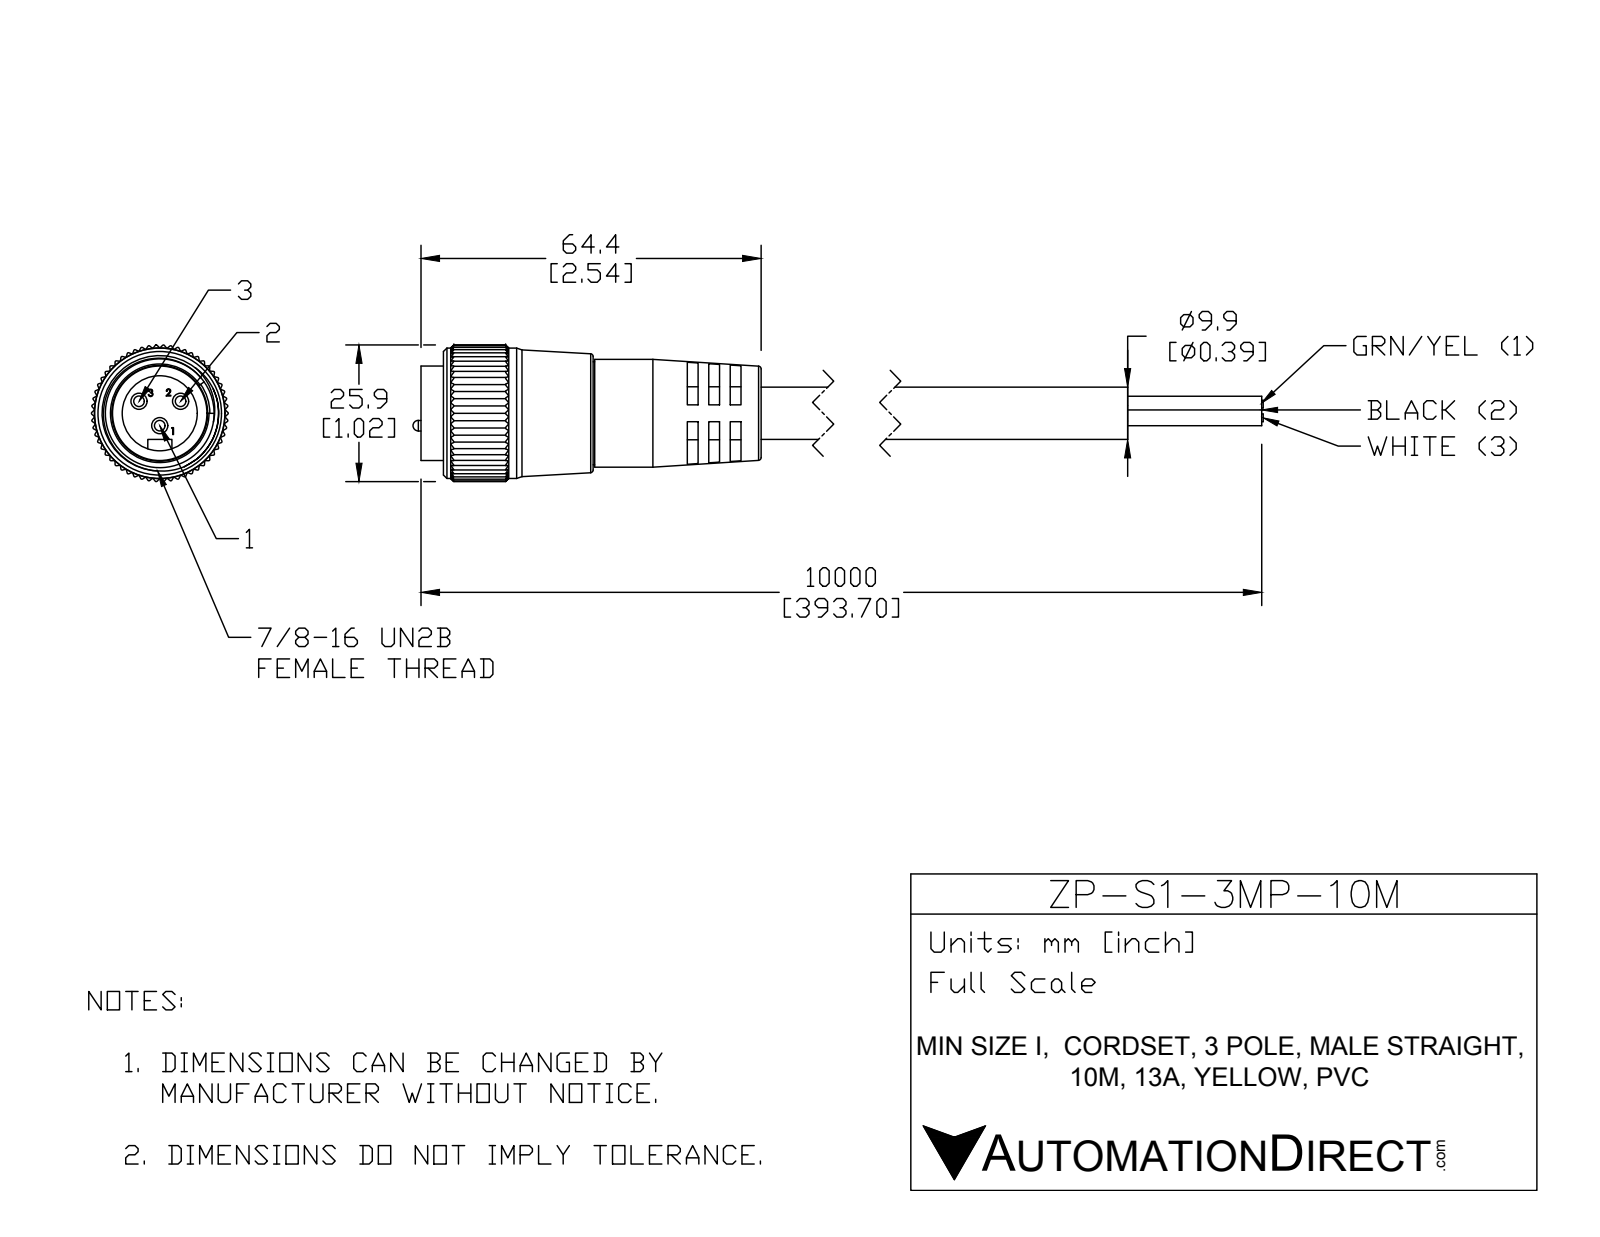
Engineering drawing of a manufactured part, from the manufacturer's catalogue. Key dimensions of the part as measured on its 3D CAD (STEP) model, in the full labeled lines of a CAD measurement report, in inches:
Part name (STEP PRODUCT): ZP-S1-3MP-10M
STEP written by: SolidWorks 2015 (AUTOMOTIVE_DESIGN)
Units: inches
Bodies: 5 solids, 564 faces (196 planar, 314 cylindrical, 54 other)
Overall size (bounding box): 4.316 × 2.083 × 1.017
Volume: 1.648 in³ · Surface area: 19.55 in²
Round holes (diameter × count): ⌀0.56 ×1, ⌀0.786 ×1, ⌀0.805 ×1, ⌀0.827 ×1
Round bosses / shafts (diameter × count): ⌀0.12 ×3, ⌀0.079 ×3, ⌀0.39 ×2, ⌀0.972 ×1, ⌀0.803 ×1, ⌀0.768 ×1, ⌀0.704 ×1
Partial cylindrical surfaces — rounded edges, fillets, slot ends (radius × count): R0.01 ×165, R0.09 ×1, R0.207 ×1, R0.509 ×1
Main face-to-face distances: 0.079, 0.159, 0.546, 0.468, 0.08, 0.387, 0.238, 0.309, 0.239, 0.317
